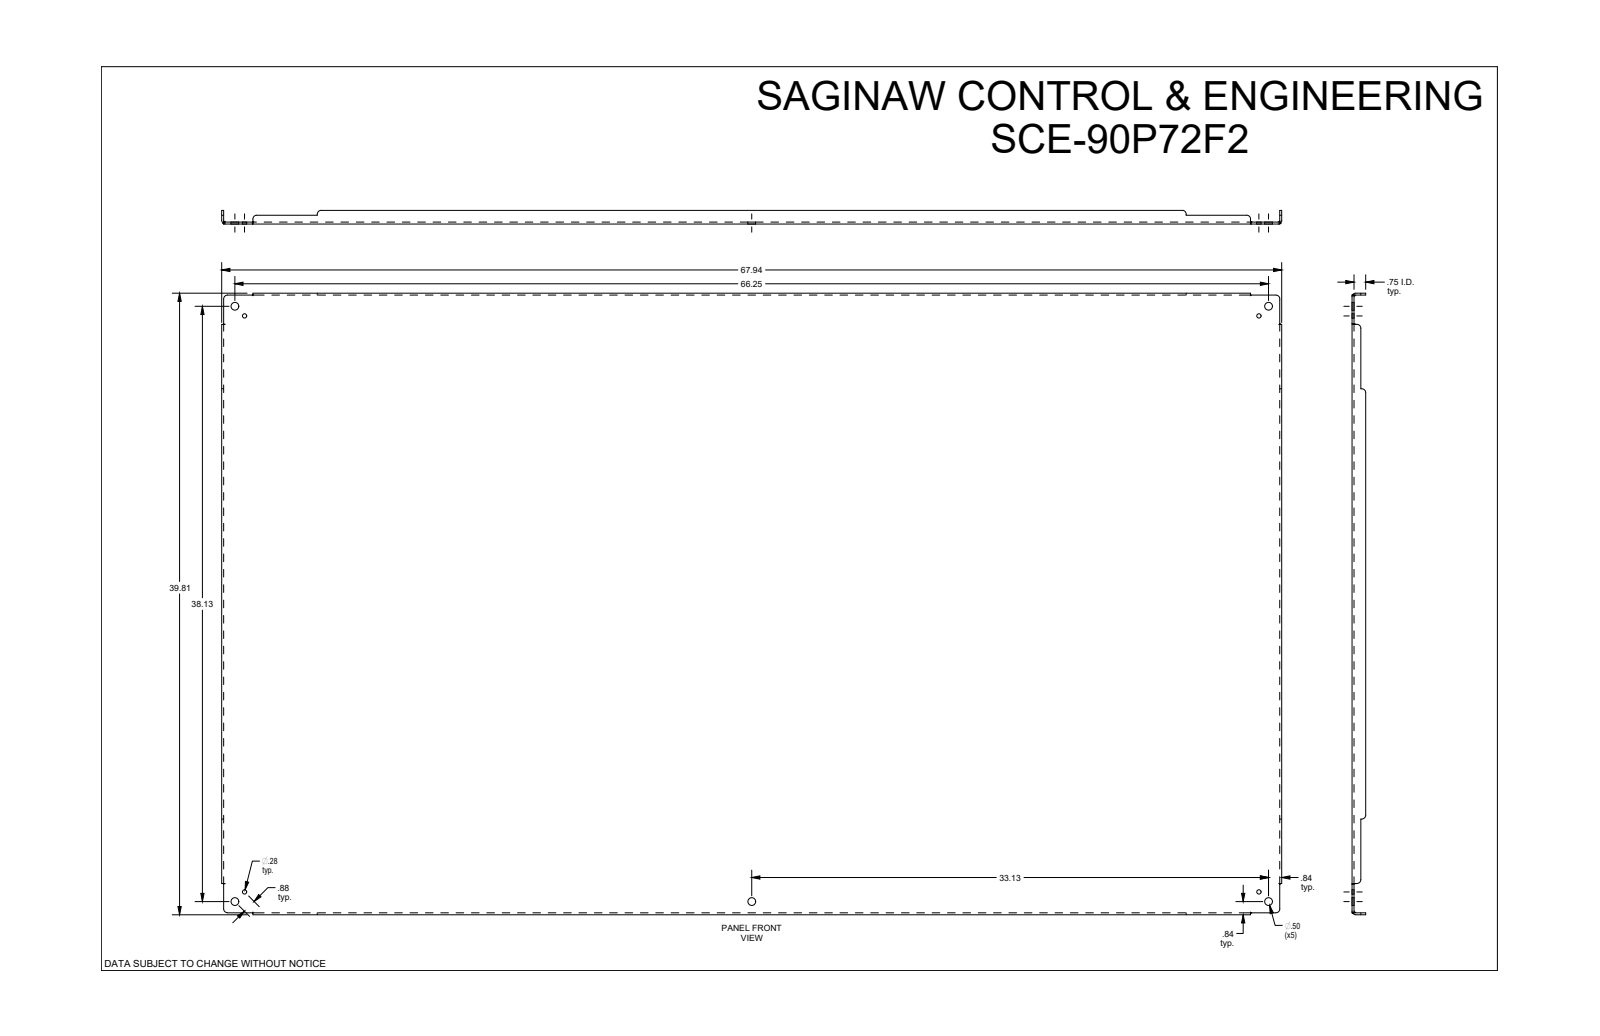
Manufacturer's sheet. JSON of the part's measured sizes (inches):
{"part_name": "SCE-90P72F2", "step_written_by": "SolidWorks 2019 (AUTOMOTIVE_DESIGN)", "units": "inches", "bodies": {"solids": 1, "faces": 107, "planar": 46, "cylindrical": 37, "other": 24}, "overall_size": [67.938, 39.813, 0.875], "volume_in3": 353.2, "surface_area_in2": 5680, "round_holes": [[0.5, 5], [0.281, 4]], "partial_cylinders_radius": [[0.25, 12], [0.112, 4], [0.237, 4]], "face_to_face_distances": [0.125, 0.125, 39.687, 67.813, 39.562, 39.813, 67.687, 0.75, 0.875, 67.938], "hole_center_spacings": [0.875, 37.511, 65.634, 75.593, 32.512, 33.125, 36.887, 38.125]}
